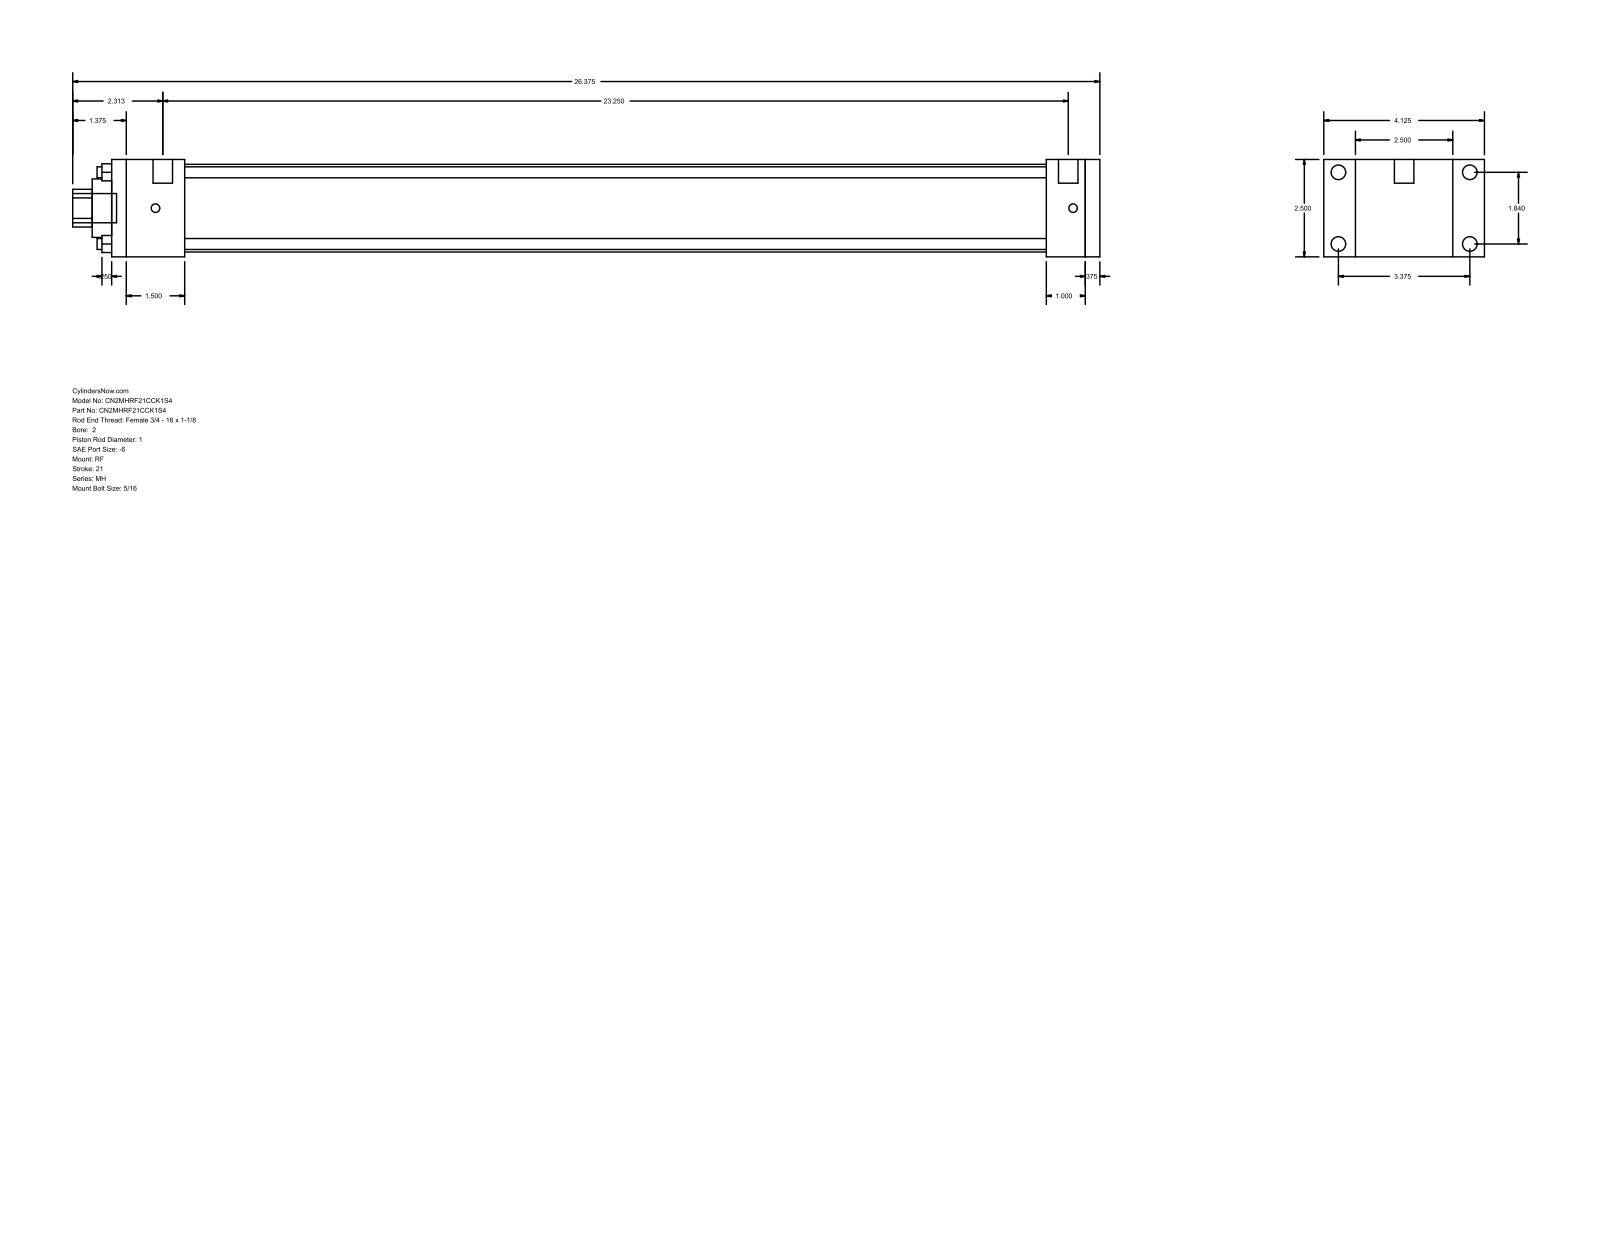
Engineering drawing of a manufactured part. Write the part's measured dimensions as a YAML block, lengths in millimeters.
part_name: "MH_RF__0200_1"
step_written_by: "GSSL Pune (CONFIG_CONTROL_DESIGN)"
units: millimeters
bodies: {solids: 0, faces: 92, planar: 64, cylindrical: 28, other: 0}
overall_size: [669.92, 104.78, 63.5]
round_holes:
  - {diameter: 7.14, count: 4}
  - {diameter: 25.4, count: 1}
  - {diameter: 38.1, count: 1}
  - {diameter: 57.15, count: 1}
round_bosses_or_shafts:
  - {diameter: 9.53, count: 4}
  - {diameter: 5.56, count: 4}
  - {diameter: 12.7, count: 2}
  - {diameter: 19.05, count: 1}
partial_cylinders:
  - {radius: 12.29, count: 1}
face_to_face_distances: [63.5, 9.52, 644.52, 635, 20.64, 25.4, 47.63, 609.6, 561.97, 587.37]
hole_center_spacings: [33.05, 46.74, 66.1]
